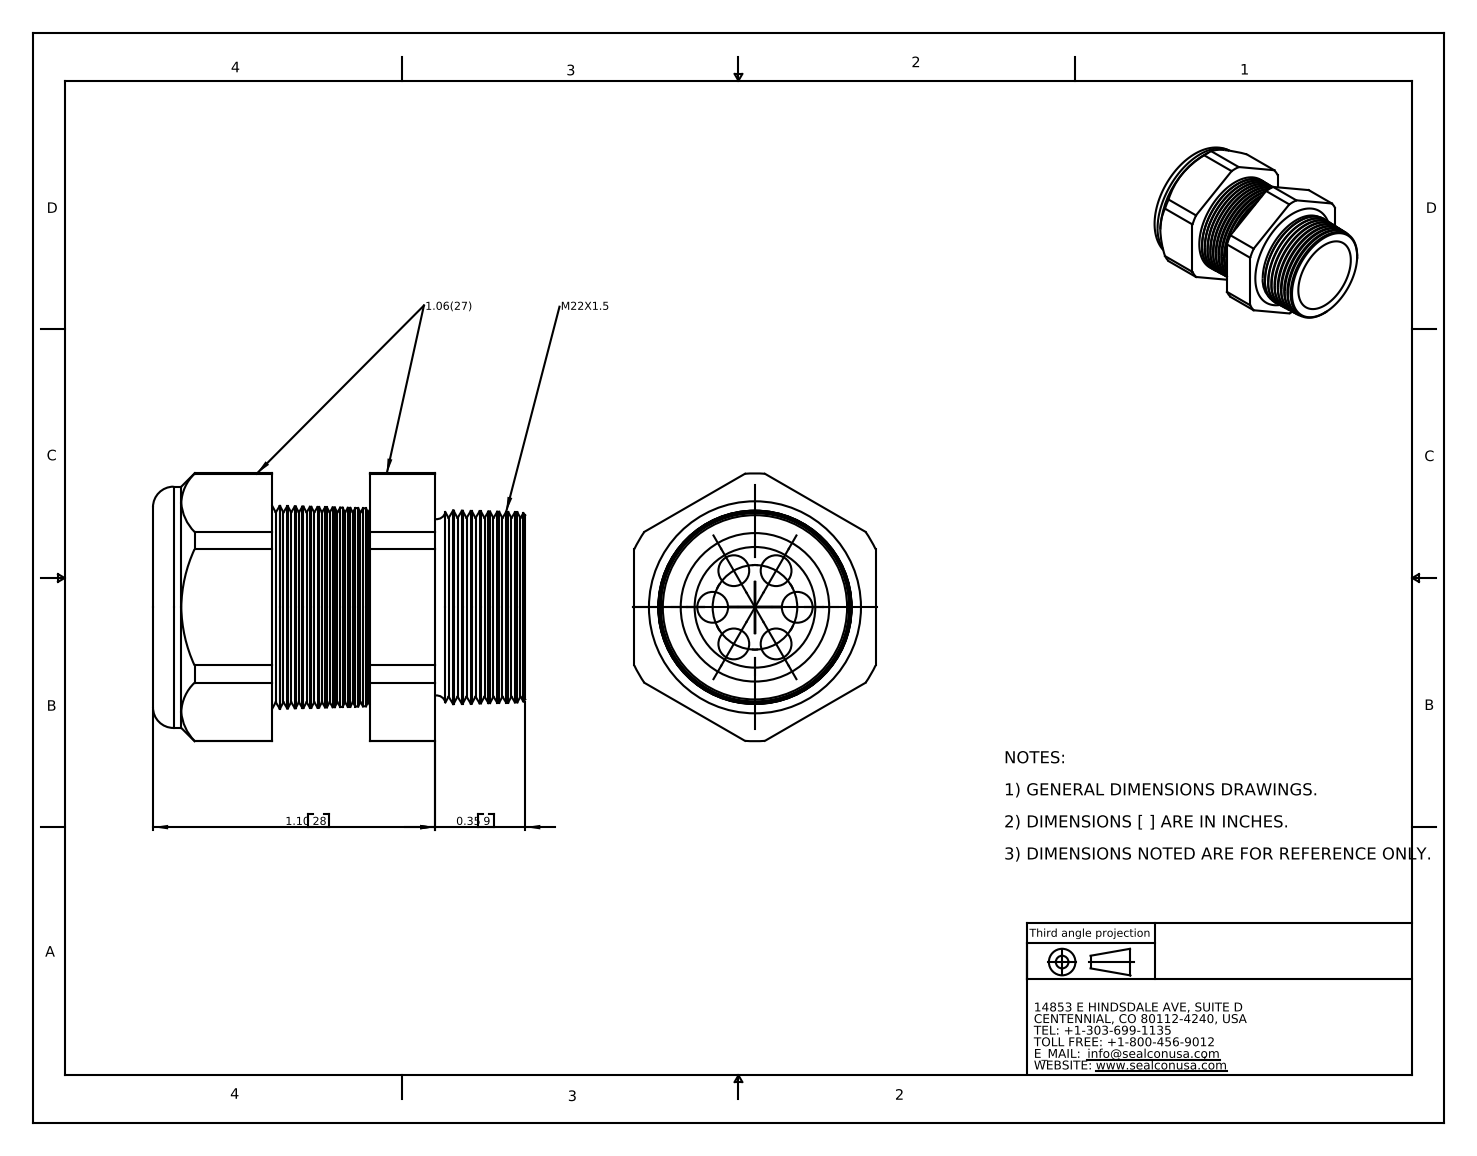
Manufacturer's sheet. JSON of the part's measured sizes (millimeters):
{"part_name": "CD22M5-BK", "step_written_by": "SolidWorks 2007 (CONFIG_CONTROL_DESIGN)", "units": "millimeters", "bodies": {"solids": 2, "faces": 198, "planar": 20, "cylindrical": 32, "other": 146}, "overall_size": [36.8, 26.5, 23.9], "volume_mm3": 9490, "surface_area_mm2": 6716, "round_holes": [[3, 6], [11.4, 1], [11.9, 1]], "round_bosses_or_shafts": [[23.9, 1]], "partial_cylinders_radius": [[13.3, 1]], "face_to_face_distances": [23.9, 21.4, 11.8, 9.7, 27.9, 16.1, 6.5, 36.8, 25, 15.4], "hole_center_spacings": [4.2, 7.2, 8.4]}
